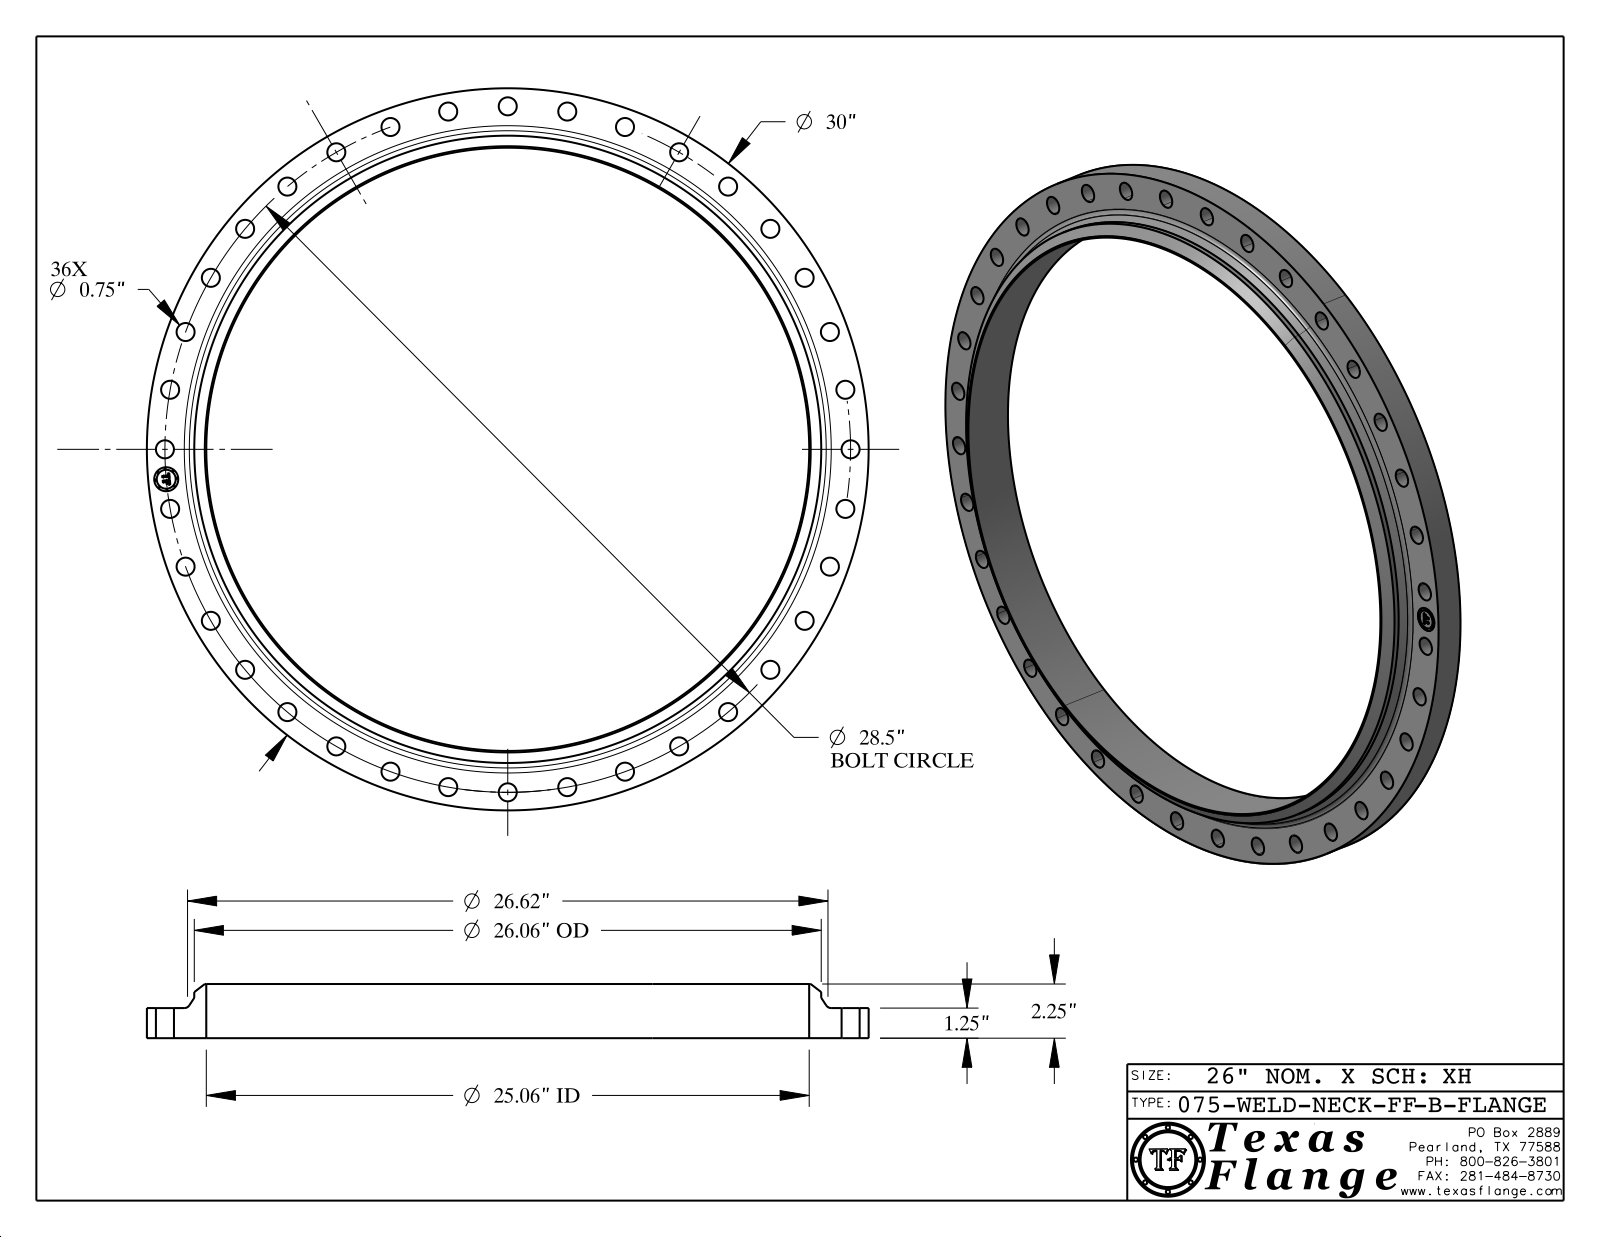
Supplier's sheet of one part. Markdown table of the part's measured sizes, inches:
| quantity | value |
| --- | --- |
| part name | 075-WELD-NECK-FF, Series B |
| STEP written by | CATIA V5 STEP AP214 (AUTOMOTIVE_DESIGN) |
| units | inches |
| bodies | 1 solid, 472 faces (368 planar, 98 cylindrical, 6 other) |
| overall size | 30 × 30 × 2.25 |
| volume | 286.5 in³ |
| surface area | 842.4 in² |
| round holes (diameter × count) | 0.75 × 36, 1 × 1, 25.06 × 1 |
| round bosses / shafts (diameter × count) | 0.061 × 8, 30 × 1, 26.06 × 1, 0.788 × 1 |
| main face-to-face distances | 1.25, 2.25, 1, 0.015, 1.235, 1.015, 0.298, 0.292, 0.054, 0.193 |
| hole center spacings | 14.25, 21.832, 9.748, 2.484, 12.044, 25.83, 7.376, 24.682 |
